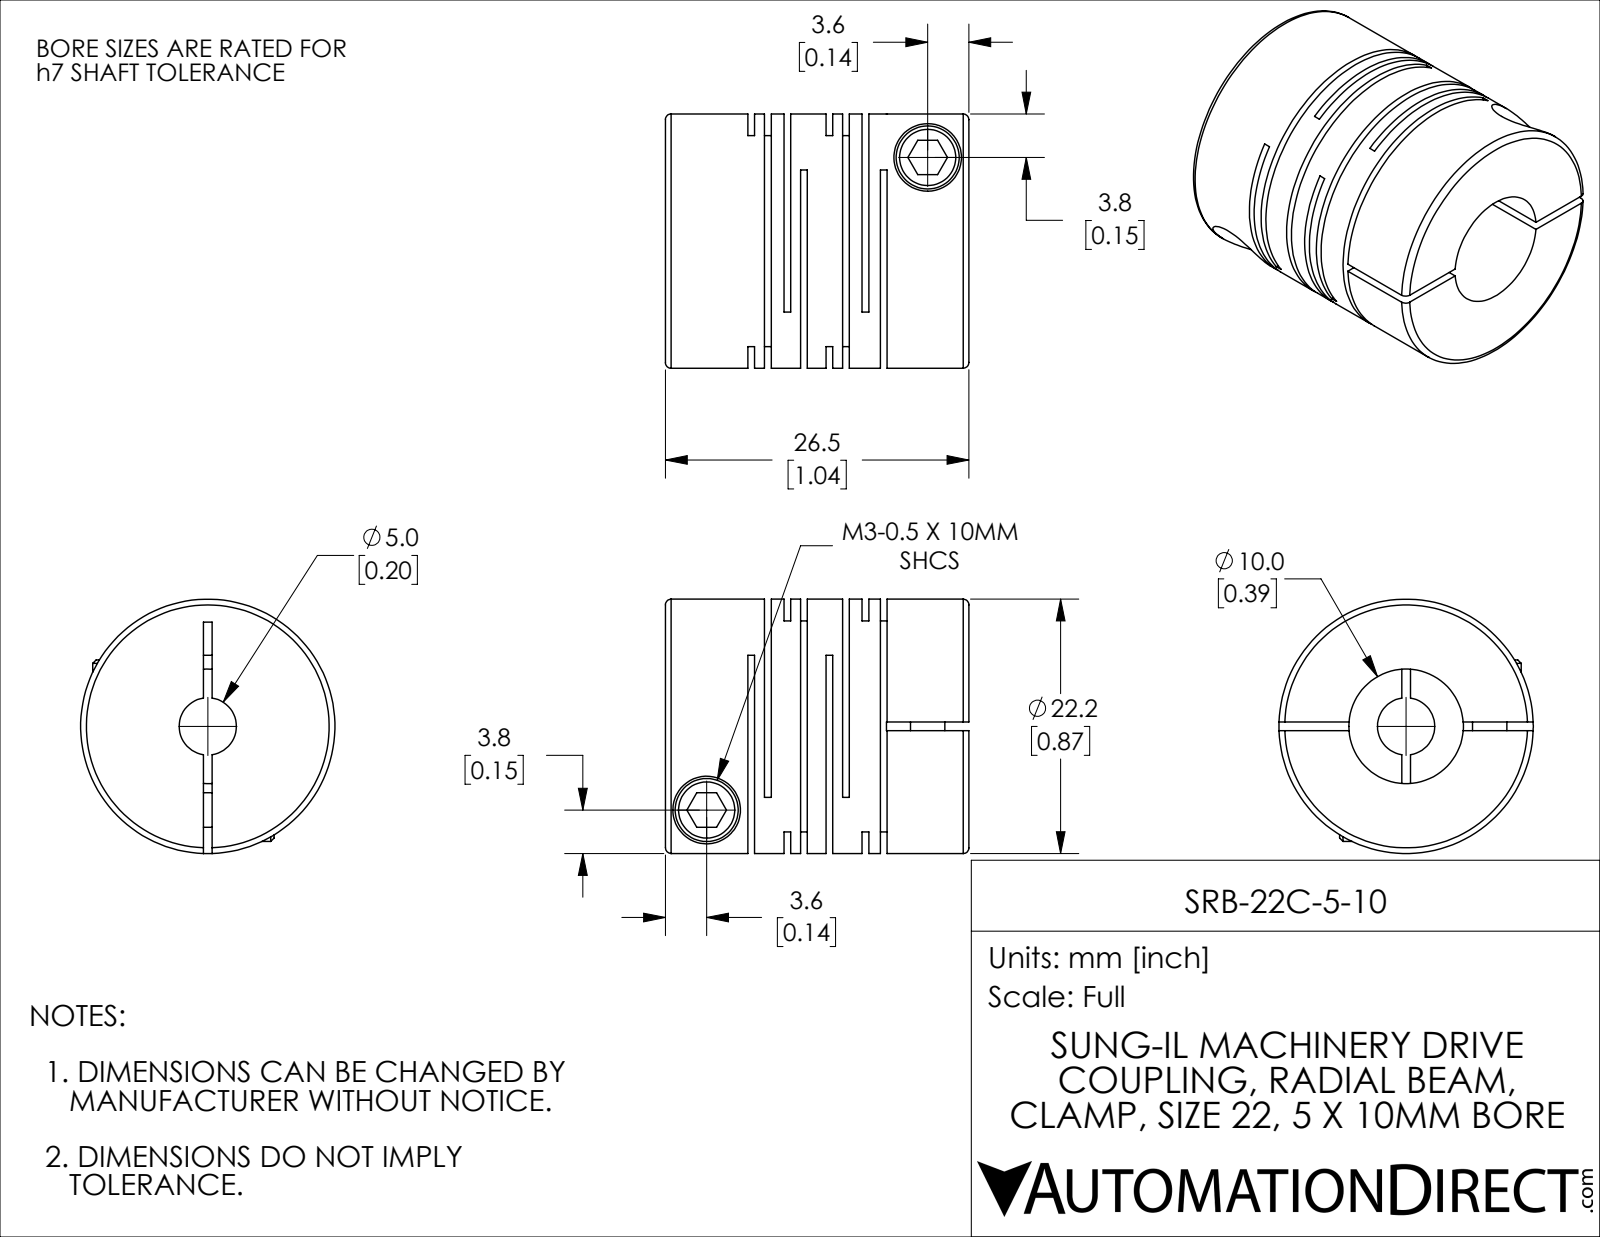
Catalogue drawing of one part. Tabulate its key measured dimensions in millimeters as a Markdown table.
| quantity | value |
| --- | --- |
| part name | SRB-22C-5-10 |
| STEP written by | SolidWorks 2021 (CONFIG_CONTROL_DESIGN) |
| units | millimeters |
| bodies | 1 solid, 115 faces (60 planar, 42 cylindrical, 13 other) |
| overall size | 26.5 × 22.2 × 22.2 |
| volume | 7 113 mm³ |
| surface area | 7 505 mm² |
| round holes (diameter × count) | 3 × 2, 5.9 × 2, 5 × 1, 10 × 1 |
| round bosses / shafts (diameter × count) | 5.5 × 2, 22.2 × 1 |
| main face-to-face distances | 0.59, 3.15, 6.82, 1.45, 5.37, 3.67, 1.7, 2.04, 3.74, 7.41 |
